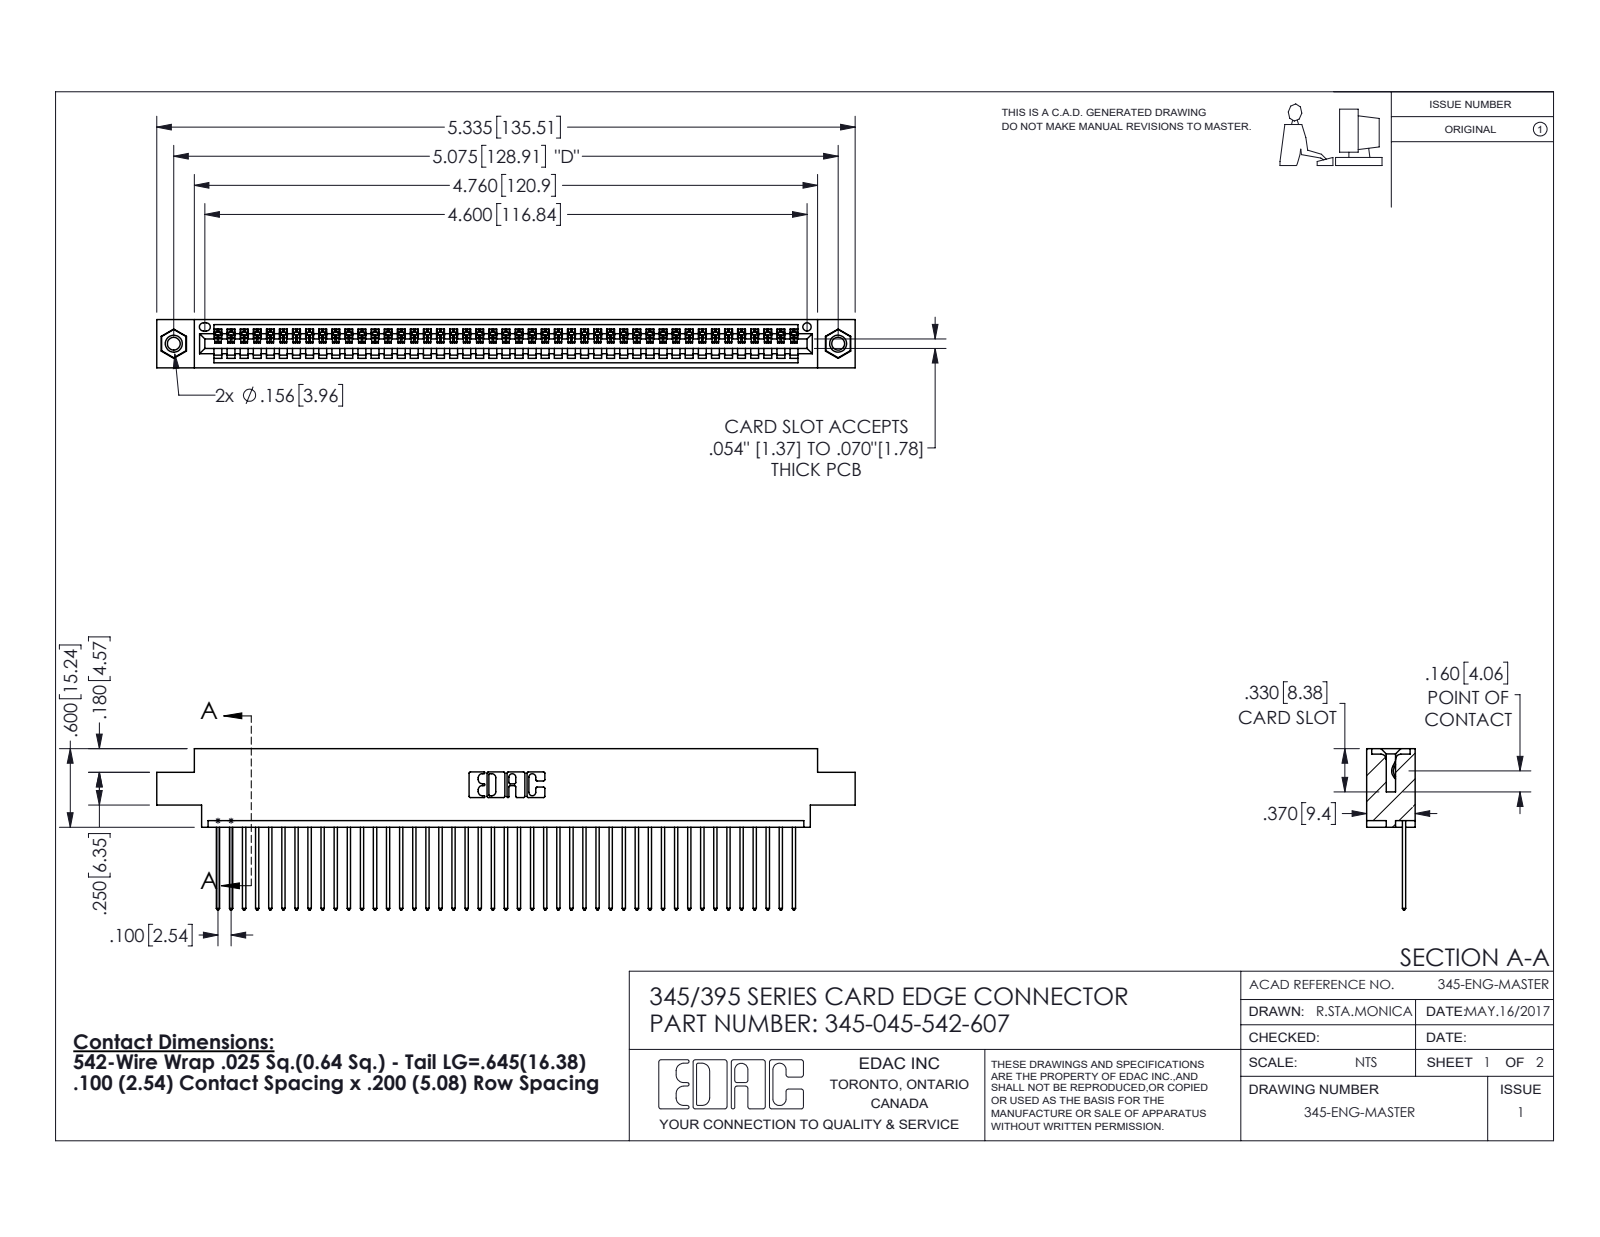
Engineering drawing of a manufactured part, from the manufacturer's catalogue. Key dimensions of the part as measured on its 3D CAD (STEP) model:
Part name (STEP PRODUCT): 345 Part_0.170 Offset - 0.156 Dia-TI; 345-045-542-607; 345-250-001_345-250-005-103; 345-292-001_345-293-142
STEP written by: SolidWorks 2016 (CONFIG_CONTROL_DESIGN)
Units: inches
Bodies: 48 solids, 2800 faces (1916 planar, 868 cylindrical, 16 other)
Overall size (bounding box): 5.335 × 1.232 × 0.37
Volume: 0.785 in³ · Surface area: 27.8 in²
Round holes (diameter × count): ⌀0.098 ×2, ⌀0.125 ×2, ⌀0.156 ×2, ⌀0.064 ×1
Round bosses / shafts (diameter × count): ⌀0.155 ×2
Partial cylindrical surfaces — rounded edges, fillets, slot ends (radius × count): R0.006 ×90, R0.01 ×90, R0.01 ×22, R0.007 ×6, R0.031 ×6, R0.026 ×3, R0.031 ×2, R0.04 ×2
Main face-to-face distances: 0.072, 0.298, 0.37, 0.098, 0.272, 0.025, 0.2, 0.225, 0.175, 0.149
Hole centre spacings: 0.27, 4.839, 5.075
